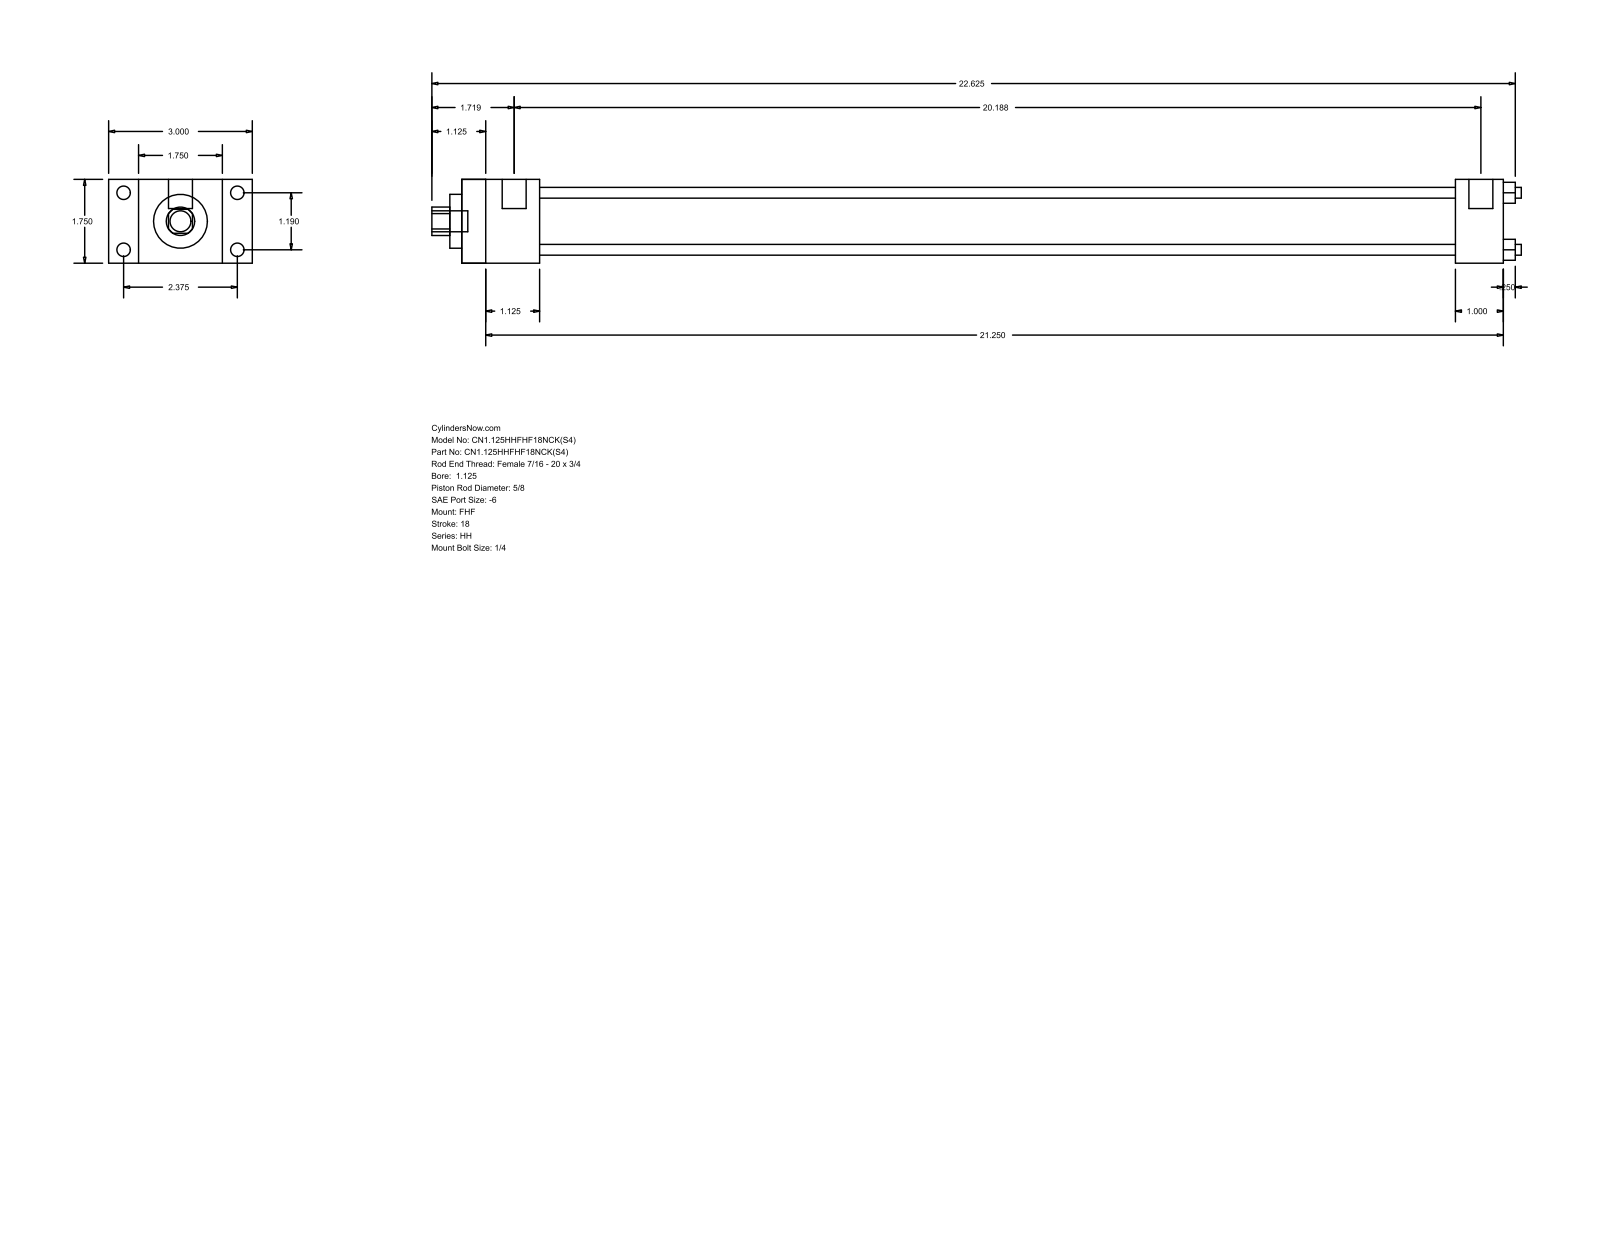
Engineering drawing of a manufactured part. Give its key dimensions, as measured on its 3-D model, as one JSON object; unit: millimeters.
{"part_name": "HH_FHF__0112_0.625", "step_written_by": "GSSL Pune (CONFIG_CONTROL_DESIGN)", "units": "millimeters", "bodies": {"solids": 0, "faces": 88, "planar": 60, "cylindrical": 28, "other": 0}, "overall_size": [577.85, 76.2, 44.45], "round_holes": [[5.71, 4], [15.88, 1], [28.57, 1], [34.92, 1]], "round_bosses_or_shafts": [[7.14, 4], [5.56, 4], [12.7, 2], [11.11, 1]], "partial_cylinders_radius": [[7.54, 1]], "face_to_face_distances": [44.46, 15.87, 60.33, 41.27, 76.2, 552.45, 511.18, 527.04, 485.77, 25.41], "hole_center_spacings": [21.37, 30.22, 42.74]}
